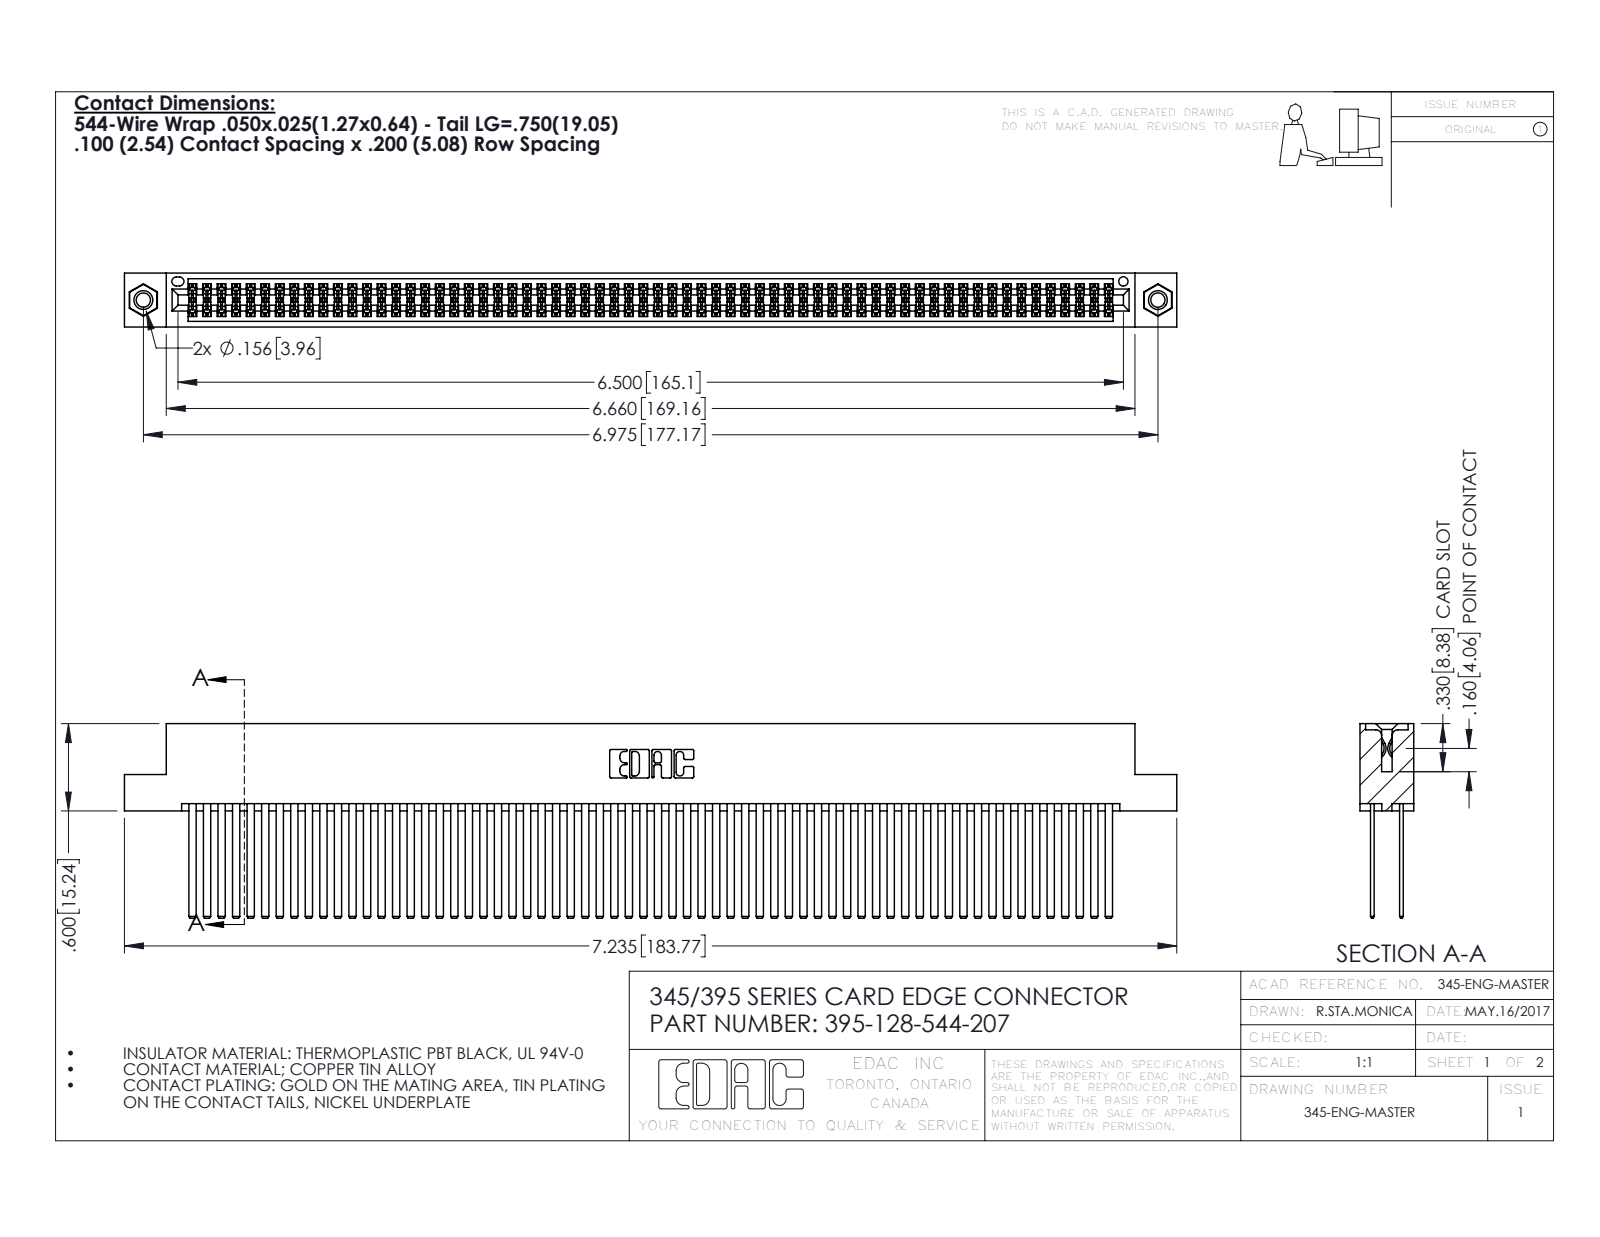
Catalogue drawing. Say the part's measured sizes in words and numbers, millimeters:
The part is named "345-250-001_345-250-005-103; 345-292-001_345-293-144; 395-128-544-207; 345 Part_Flush Mounting Lugs - 0.156 Dia-TI". Its 3-D file was written by "SolidWorks 2016 (CONFIG_CONTROL_DESIGN)". It is 131 solids with 5818 faces: 3824 planar, 1978 cylindrical and 16 other. Overall it measures 183.8 by 34 by 9.4 millimeters. Its volume is 19 830 cubic millimeters and its surface area 35 030 square millimeters. Round holes: 2 of diameter 2.5, 2 of diameter 3.2, 2 of diameter 4, 1 of diameter 1.6. Round bosses or shafts: 2 of diameter 3.9. Partial cylindrical surfaces (rounded edges, fillets, slot ends): 192 of radius 0.2, 22 of radius 0.3, 6 of radius 0.2, 6 of radius 0.8, 3 of radius 0.7, 2 of radius 0.4, 2 of radius 0.5, 2 of radius 0.6. The main face-to-face distances are 5.1, 0.6, 1.8, 2.5, 6.9, 7.6, 5.7, 4.4, 9.4, 1.3. The hole center spacings are 6.9, 171.2, 177.2.
